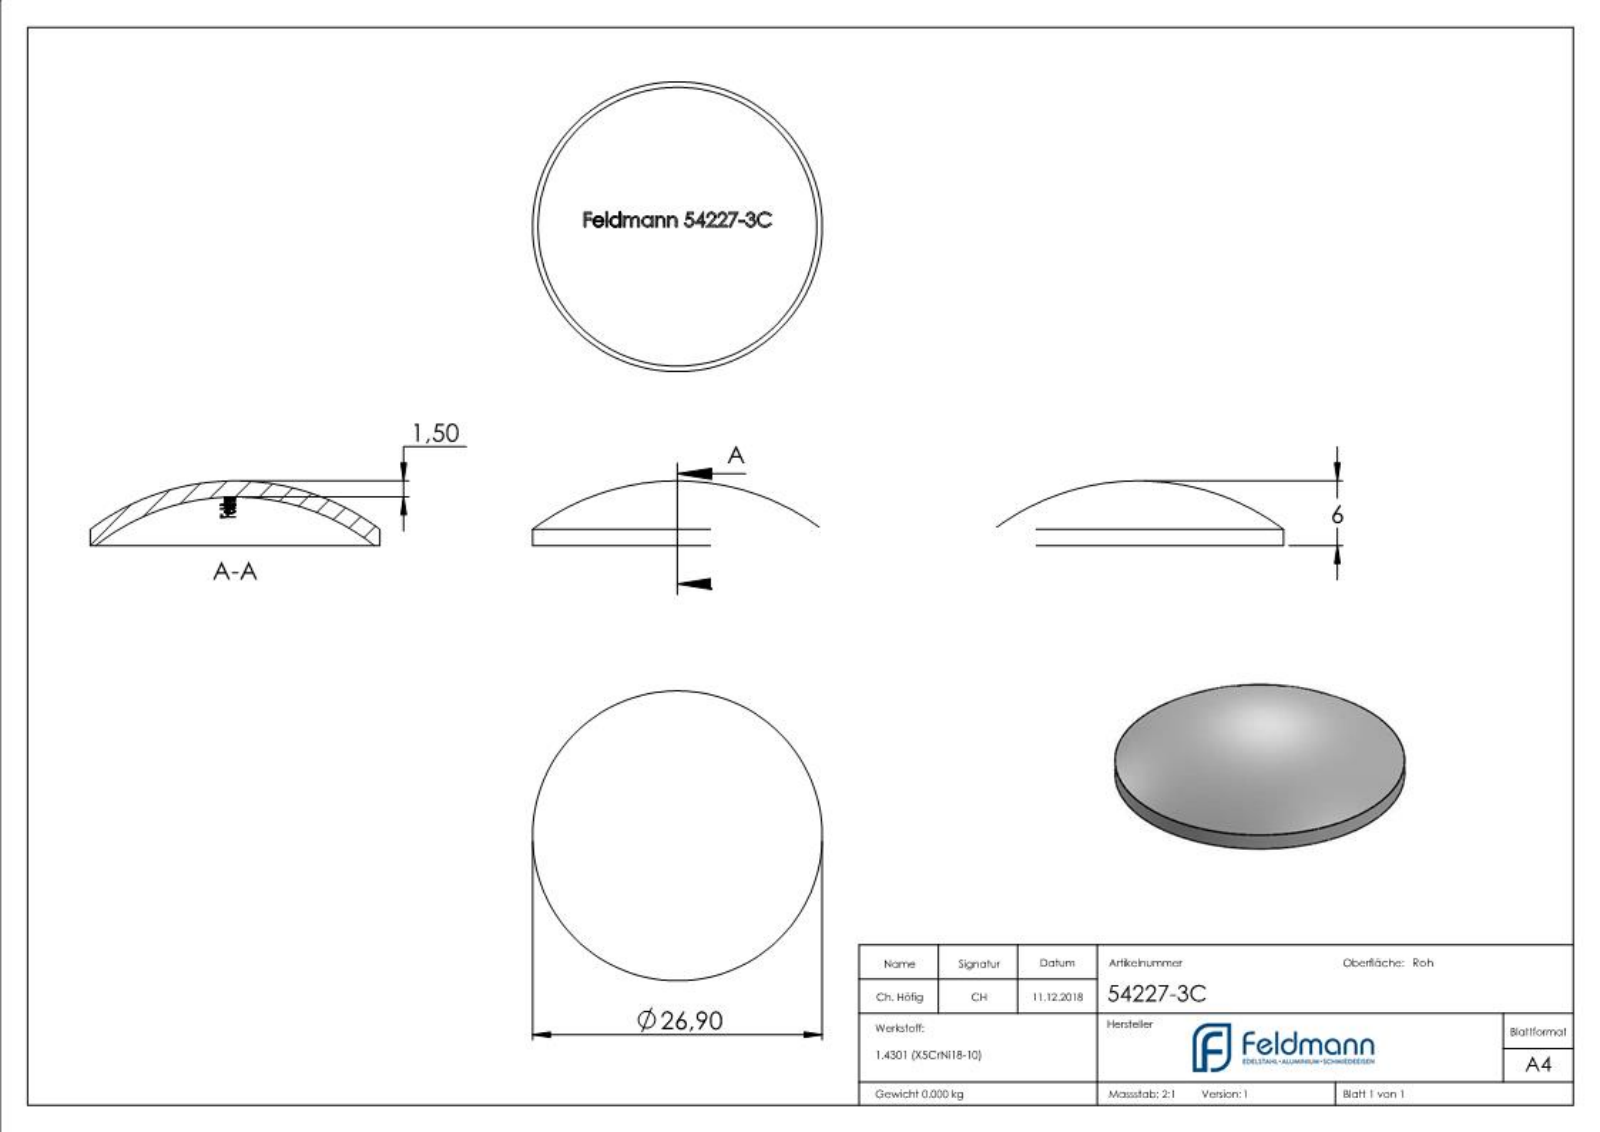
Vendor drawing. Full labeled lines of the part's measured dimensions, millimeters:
Part name (STEP PRODUCT): 54227-3C
STEP written by: SolidWorks 2015 (CONFIG_CONTROL_DESIGN)
Units: millimetres
Bodies: 4 solids, 237 faces (101 planar, 2 cylindrical, 134 other)
Overall size (bounding box): 26.9 × 26.9 × 6
Volume: 947 mm³ · Surface area: 1 400 mm²
Round bosses / shafts (diameter × count): ⌀26.9 ×1
Main face-to-face distances: 0.39, 2.97, 1.32, 1.12, 2.02, 1.25, 8.92, 1.64, 0.44, 1.05
